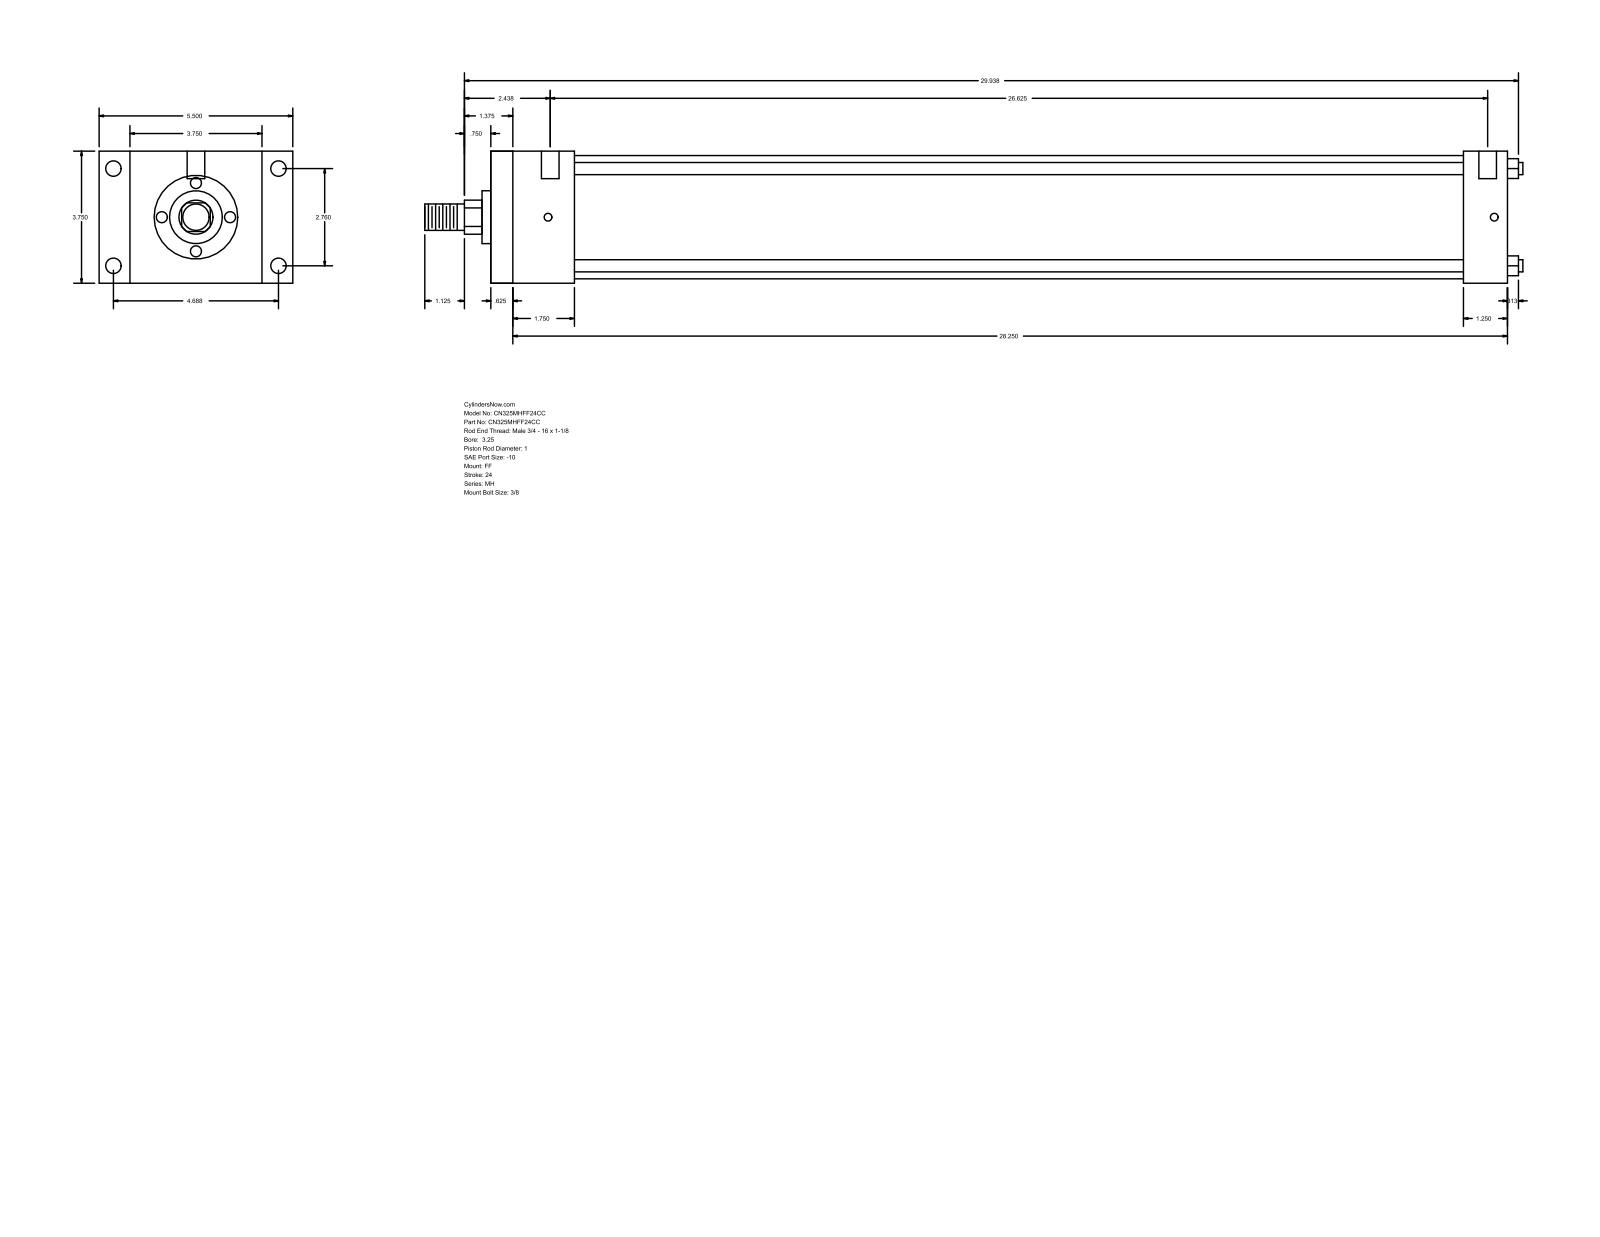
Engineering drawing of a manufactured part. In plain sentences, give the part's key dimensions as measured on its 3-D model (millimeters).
The part is named "MH_FF__0325_1". Its 3-D file was written by "GSSL Pune (CONFIG_CONTROL_DESIGN)". It is 0 solids with 92 faces: 64 planar, 28 cylindrical and 0 other. Overall it measures 792.16 by 139.7 by 95.25 millimeters. Round holes: 4 of diameter 5.56, 4 of diameter 11.13, 2 of diameter 12.7. Round bosses or shafts: 4 of diameter 8.76, 1 of diameter 88.9, 1 of diameter 38.1, 1 of diameter 25.4, 1 of diameter 19.05. Partial cylindrical surfaces (rounded edges, fillets, slot ends): 1 of radius 12.29. The main face-to-face distances are 95.24, 733.43, 15.87, 717.56, 22.23, 117.47, 701.68, 685.81, 31.75, 60.33. The hole center spacings are 70.1, 119.06, 138.16, 682.62, 1.58, 4.76, 676.28, 677.86.
